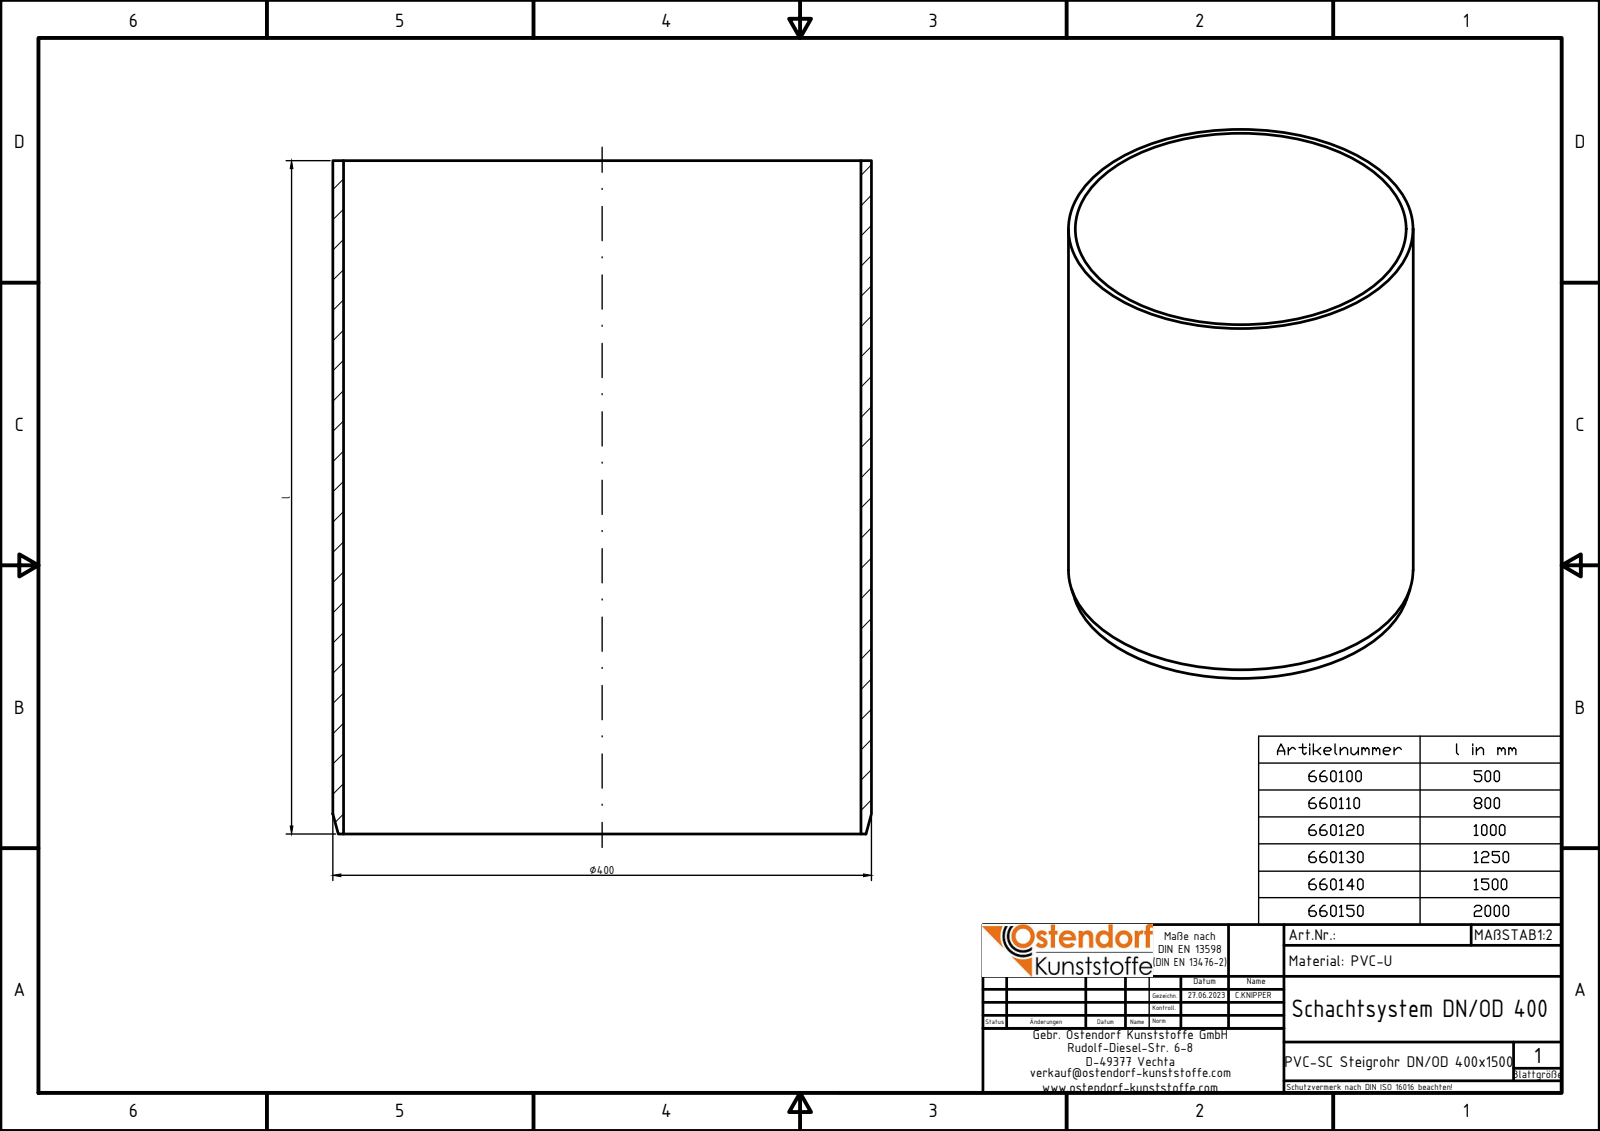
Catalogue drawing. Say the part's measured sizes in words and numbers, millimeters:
The part is named "660140". Its 3-D file was written by "Autodesk Inventor 2020 (AUTOMOTIVE_DESIGN)". It is 1 solid with 5 faces: 2 planar, 2 cylindrical and 1 other. Overall it measures 1500 by 400 by 400 millimeters. Its volume is 14 560 000 cubic millimeters and its surface area 3 710 000 square millimeters. Round holes: 1 of diameter 384.2. Round bosses or shafts: 1 of diameter 400. The main face-to-face distances are 1500.
